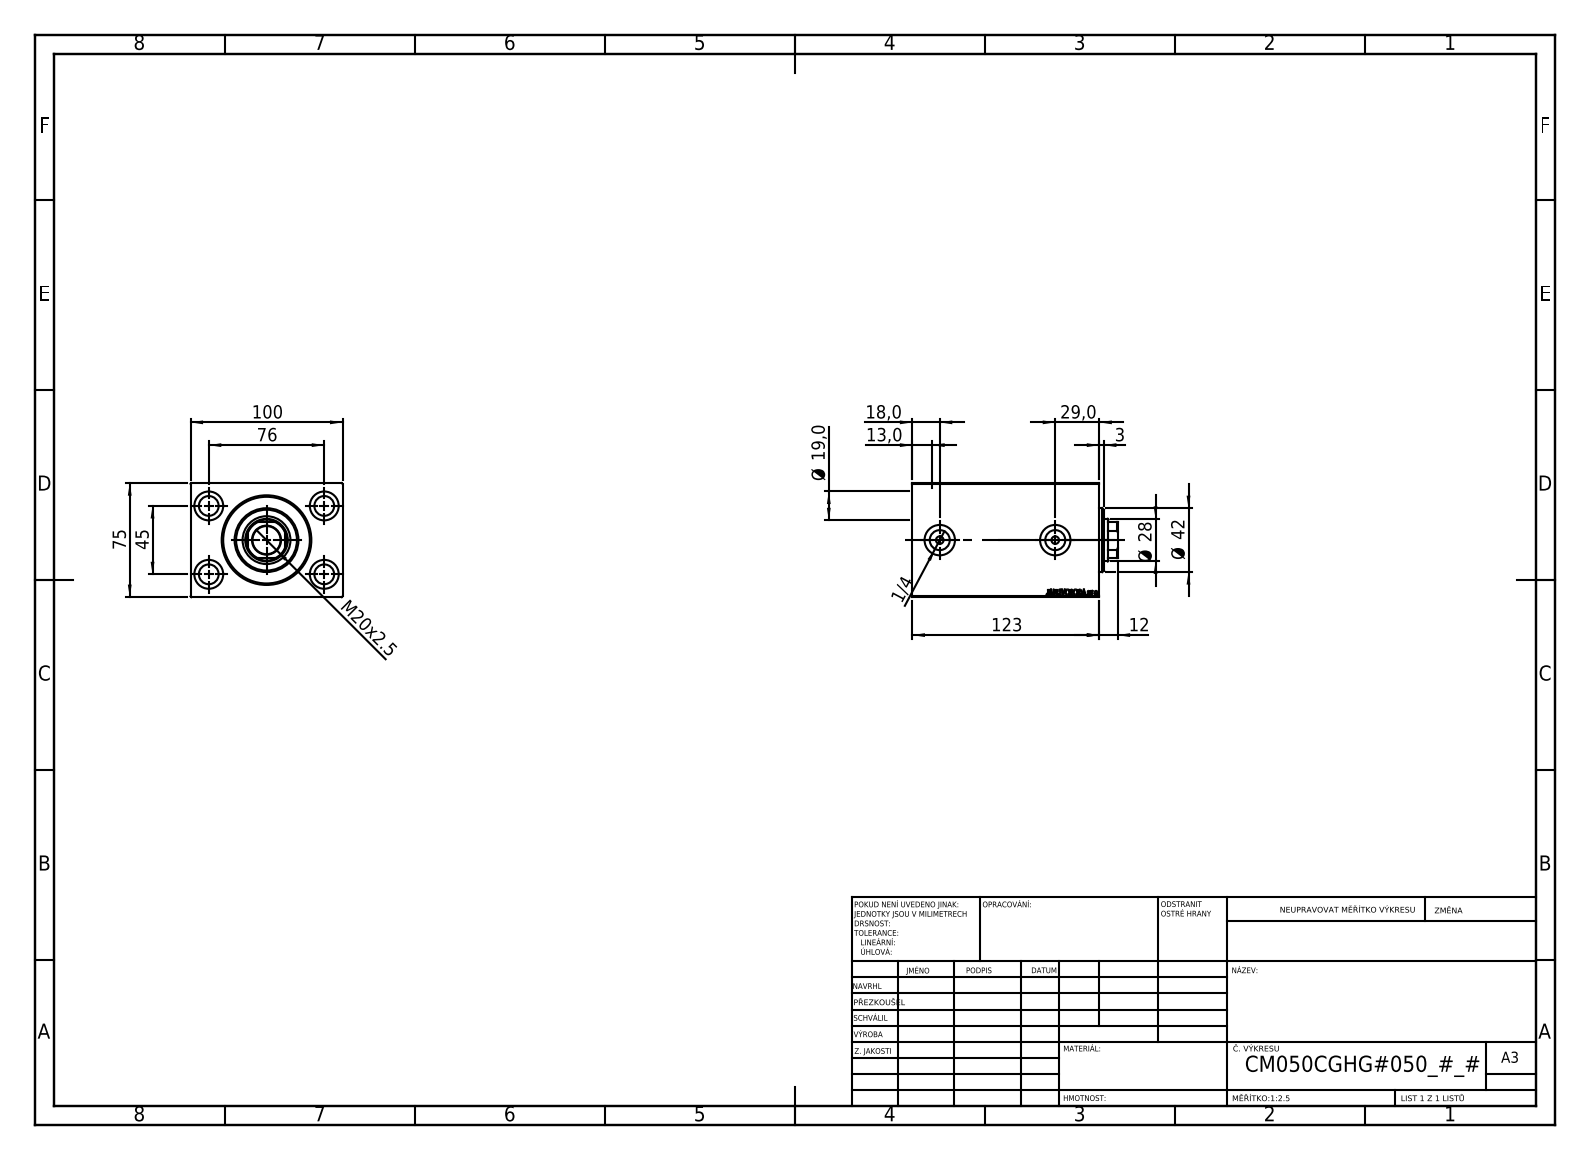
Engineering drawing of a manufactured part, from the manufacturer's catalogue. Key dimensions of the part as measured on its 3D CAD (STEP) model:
Part name (STEP PRODUCT): V450CM_C_VCP; V450CM_C_Body; V450CM_VC_B
STEP written by: SolidWorks 2019 (CONFIG_CONTROL_DESIGN)
Units: millimetres
Bodies: 3 solids, 865 faces (409 planar, 62 cylindrical, 394 other)
Overall size (bounding box): 135 × 100 × 75
Volume: 771 502 mm³ · Surface area: 124 408 mm²
Round holes (diameter × count): ⌀13 ×4, ⌀19 ×4, ⌀5 ×2, ⌀13.16 ×2, ⌀20 ×2, ⌀18.5 ×1, ⌀28 ×1, ⌀31.5 ×1, ⌀50 ×1, ⌀52 ×1, ⌀57 ×1
Round bosses / shafts (diameter × count): ⌀42 ×1
Partial cylindrical surfaces — rounded edges, fillets, slot ends (radius × count): R13.5 ×1
Main face-to-face distances: 75, 100, 123, 109, 14, 97, 12, 111, 62, 13
Hole centre spacings: 44.16, 76, 45, 88.32
